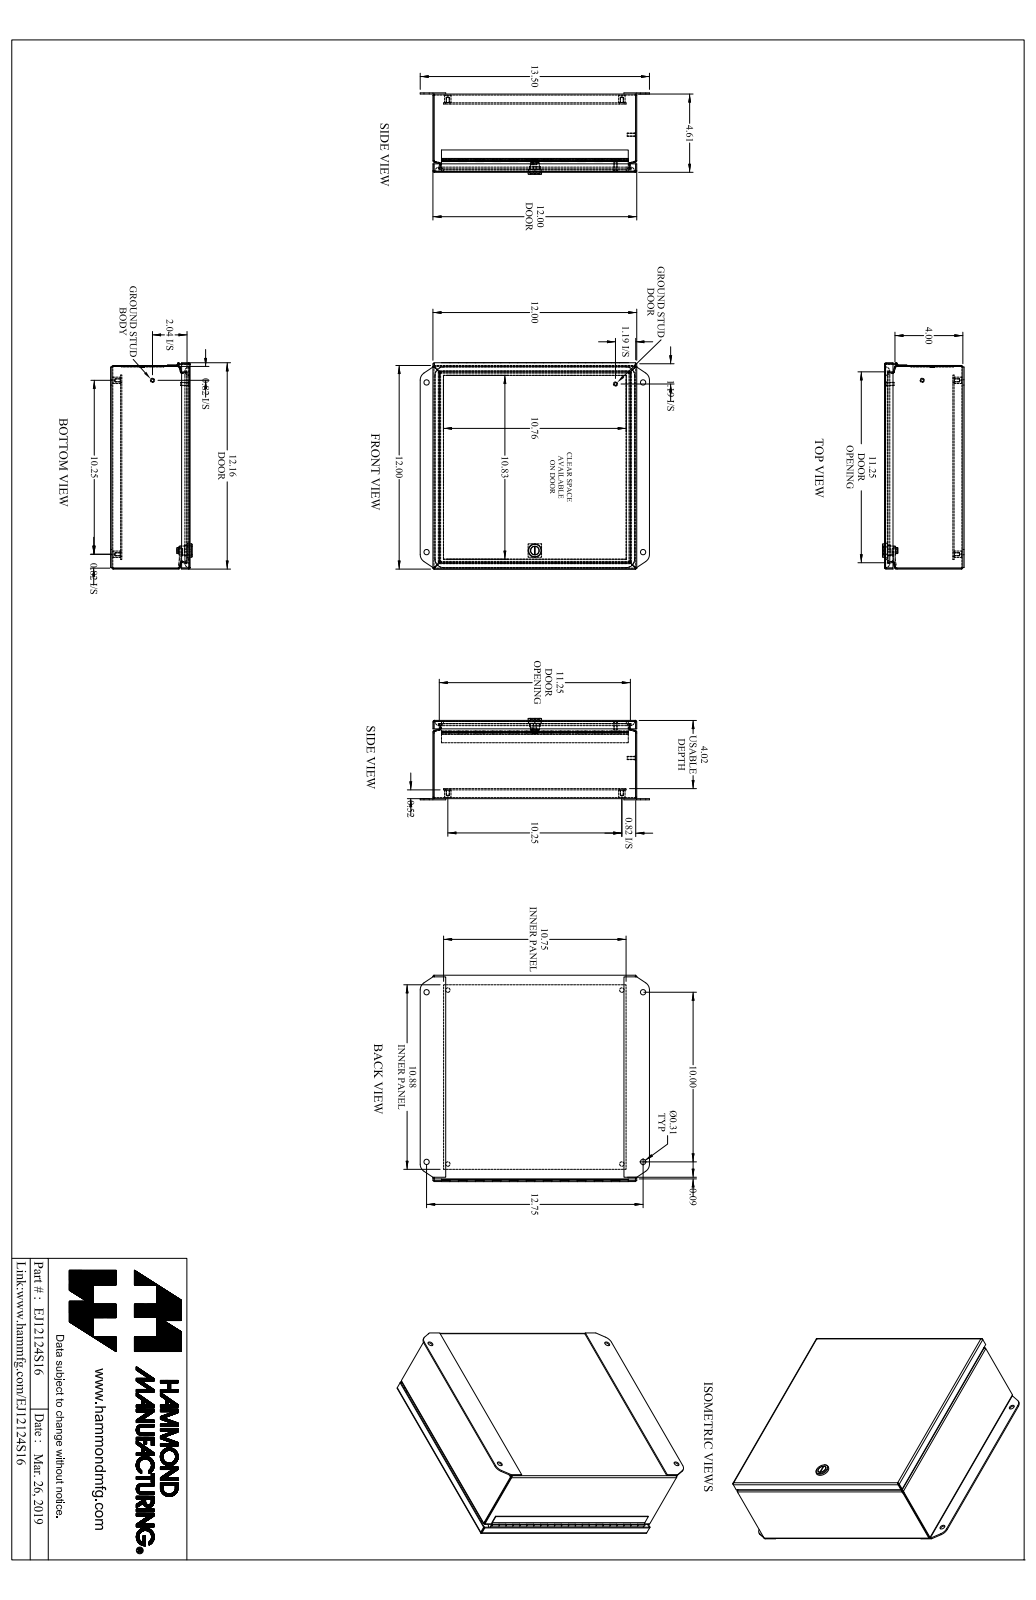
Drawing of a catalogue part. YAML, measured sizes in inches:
part_name: "EJ12124S16_Default"
step_written_by: "SolidWorks 2019 (CONFIG_CONTROL_DESIGN)"
units: inches
bodies: {solids: 16, faces: 628, planar: 326, cylindrical: 222, other: 80}
overall_size: [13.5, 12.165, 4.805]
volume: 46.36
surface_area: 1519
round_holes:
  - {diameter: 0.156, count: 4}
  - {diameter: 0.265, count: 4}
  - {diameter: 0.313, count: 4}
  - {diameter: 0.05, count: 1}
  - {diameter: 0.516, count: 1}
round_bosses_or_shafts:
  - {diameter: 0.375, count: 4}
  - {diameter: 0.25, count: 2}
  - {diameter: 0.19, count: 2}
  - {diameter: 0.788, count: 1}
  - {diameter: 0.535, count: 1}
  - {diameter: 0.496, count: 1}
  - {diameter: 0.435, count: 1}
  - {diameter: 0.1, count: 1}
partial_cylinders:
  - {radius: 0.029, count: 16}
  - {radius: 0.086, count: 16}
  - {radius: 0.281, count: 12}
  - {radius: 0.25, count: 4}
  - {radius: 0.499, count: 4}
  - {radius: 0.5, count: 4}
  - {radius: 0.06, count: 2}
  - {radius: 0.03, count: 1}
face_to_face_distances: [0.057, 4.554, 11.943, 0.072, 0.589, 4.611, 4.497, 4.094, 4.037, 0.46]
hole_center_spacings: [1.256, 10.202, 10.25, 11.501, 15.322, 5.13, 6.376, 10]
